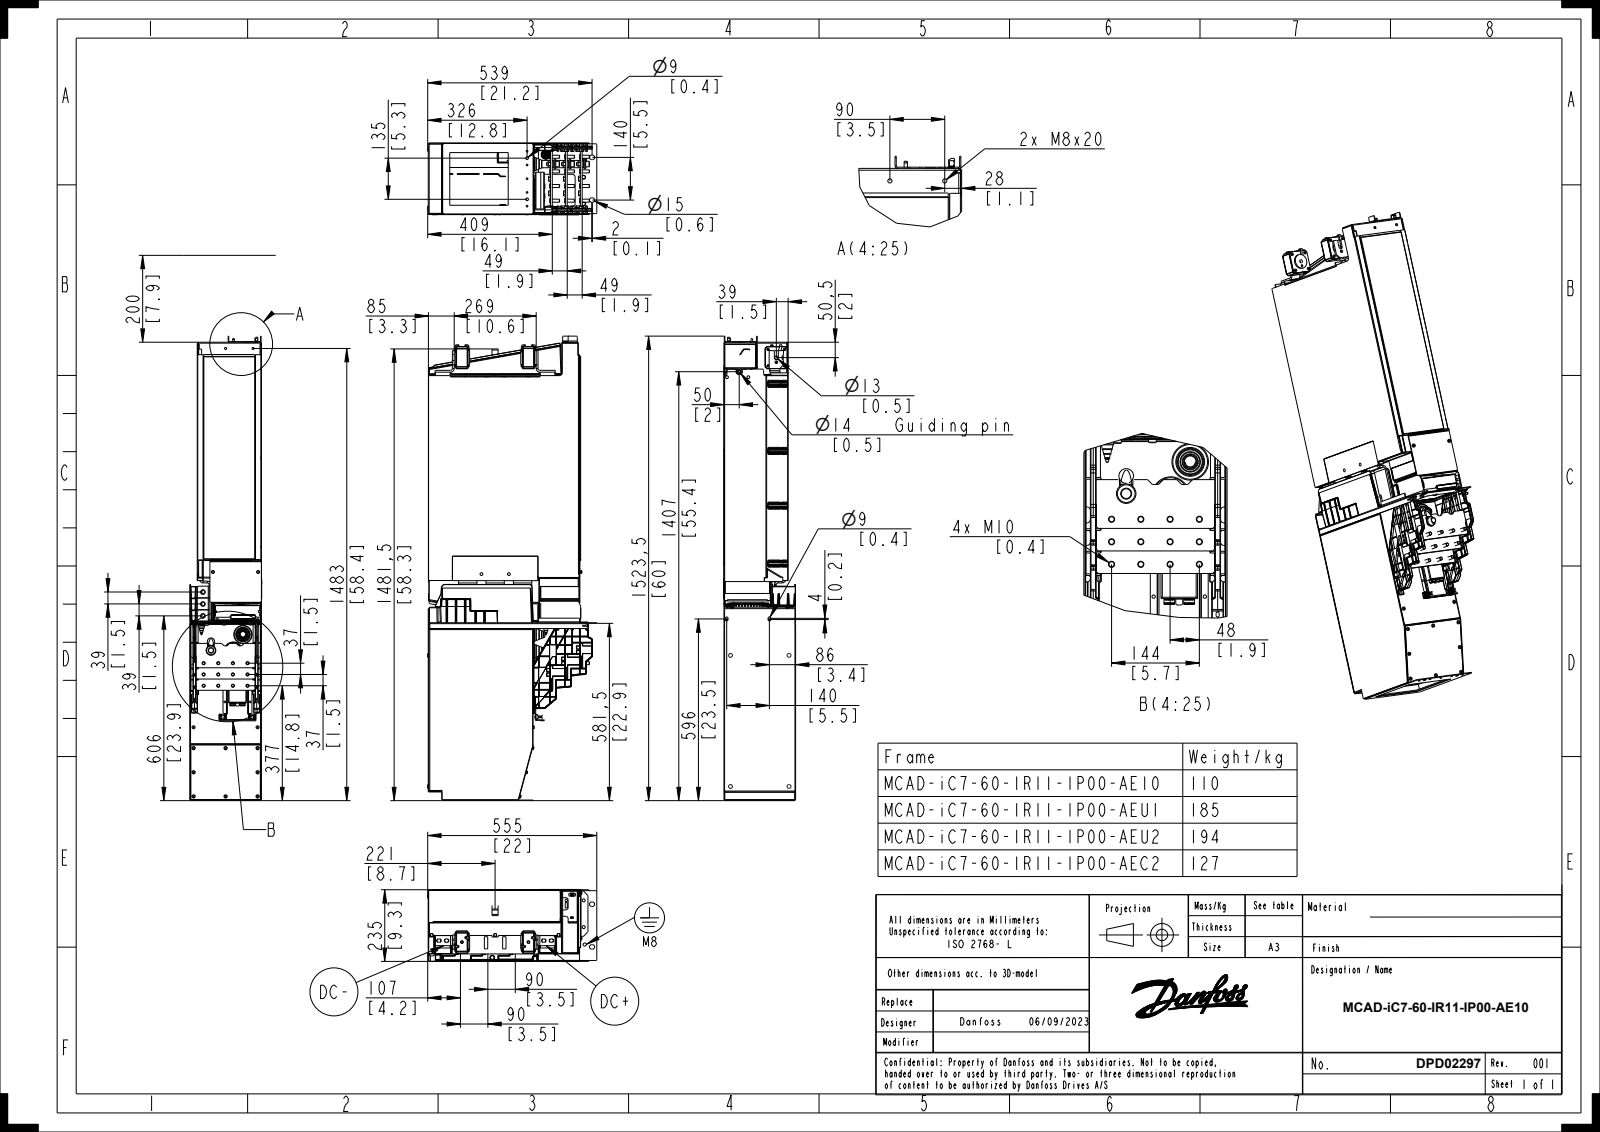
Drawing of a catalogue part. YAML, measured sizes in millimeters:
part_name: "141H7682_PRT2; 70CMC1114660_2; 141H7682_ASM; AR11-IR11_3 (+3 more)"
step_written_by: "CREO PARAMETRIC BY PTC INC, 2022124 (CONFIG_CONTROL_DESIGN)"
units: millimeters
bodies: {solids: 3, faces: 13870, planar: 7166, cylindrical: 3520, other: 3184}
overall_size: [1523.5, 554.78, 236.69]
round_holes:
  - {diameter: 6, count: 8}
  - {diameter: 12.5, count: 7}
  - {diameter: 5.5, count: 5}
  - {diameter: 3.3, count: 4}
  - {diameter: 10, count: 4}
  - {diameter: 10.47, count: 3}
  - {diameter: 15, count: 3}
  - {diameter: 5, count: 2}
  - {diameter: 6.8, count: 2}
  - {diameter: 9, count: 2}
  - {diameter: 10.58, count: 2}
  - {diameter: 75, count: 2}
round_bosses_or_shafts:
  - {diameter: 5, count: 39}
  - {diameter: 10, count: 25}
  - {diameter: 7.5, count: 15}
  - {diameter: 8, count: 12}
  - {diameter: 3, count: 5}
  - {diameter: 31.2, count: 4}
  - {diameter: 60, count: 3}
  - {diameter: 32, count: 3}
partial_cylinders:
  - {radius: 1, count: 846}
  - {radius: 0.5, count: 438}
  - {radius: 2, count: 419}
  - {radius: 3, count: 122}
  - {radius: 1.5, count: 91}
  - {radius: 0.4, count: 66}
  - {radius: 5, count: 65}
  - {radius: 4, count: 63}
face_to_face_distances: [1.5, 2, 209, 0.5, 233, 138.5, 207.5, 210.5, 436, 69]
hole_center_spacings: [15, 22.5, 45, 90, 81.95, 135, 194.69, 210.03]
